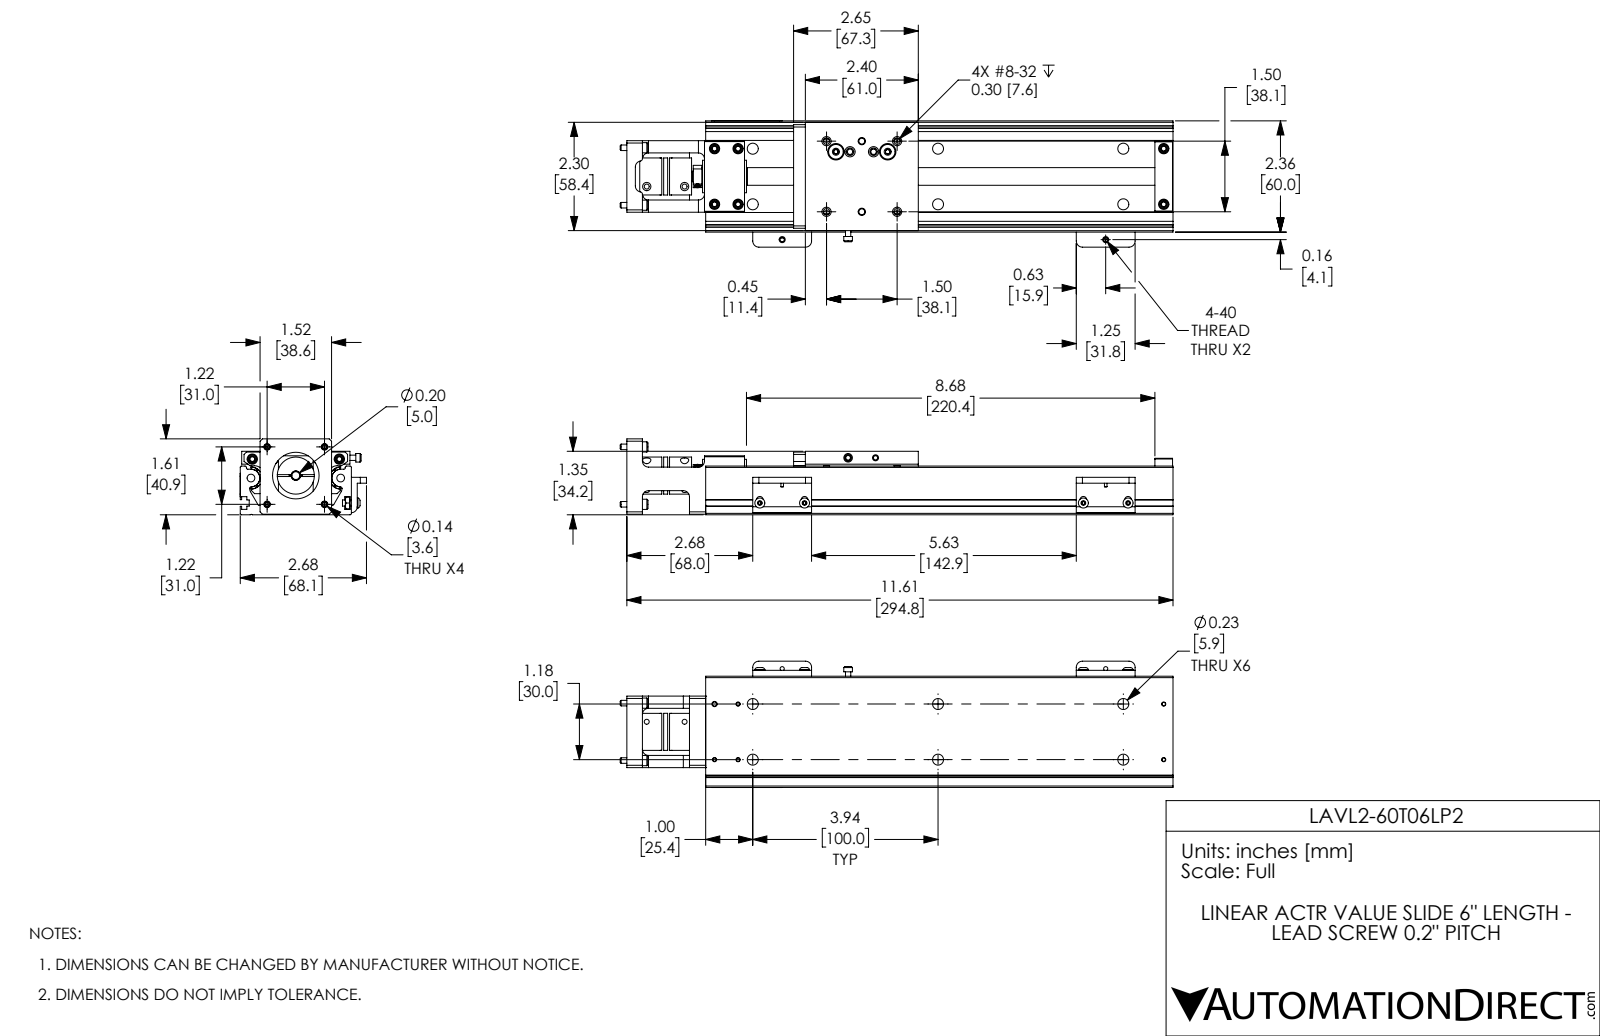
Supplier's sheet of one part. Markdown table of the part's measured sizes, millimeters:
| quantity | value |
| --- | --- |
| part name | LAVL2-60T06LP2; LAVL2-60T06LP2_BLOCK; LAVL2-60T06LP2_BODY |
| STEP written by | SolidWorks 2017 (AUTOMOTIVE_DESIGN) |
| units | millimeters |
| bodies | 52 solids, 2124 faces (1295 planar, 521 cylindrical, 308 other) |
| overall size | 298.4 × 68.1 × 40.9 |
| volume | 266 900 mm³ |
| surface area | 144 600 mm² |
| round holes (diameter × count) | 2.3 × 18, 3.6 × 10, 5.6 × 10, 3.5 × 6, 5.9 × 6, 3.6 × 4, 0.8 × 2, 2.5 × 2, 2.7 × 2, 3.2 × 2, 4 × 2, 4.2 × 2 |
| round bosses / shafts (diameter × count) | 2.8 × 15, 4.6 × 11, 5.5 × 4, 5.4 × 4, 3 × 4, 7.9 × 2, 4.8 × 2, 4.2 × 2 |
| partial cylindrical surfaces (radius × count) | 3.3 × 20, 0.8 × 12, 1.8 × 8, 1.5 × 4, 0.5 × 3, 1 × 2, 1.3 × 2, 1.7 × 2 |
| main face-to-face distances | 5.1, 60, 34.2, 29.2, 10.7, 49.3, 3.6, 2.9, 4.7, 7.1 |
| hole center spacings | 30, 38.1, 19.1, 21.8, 21.9, 42.6, 100, 104.4 |
